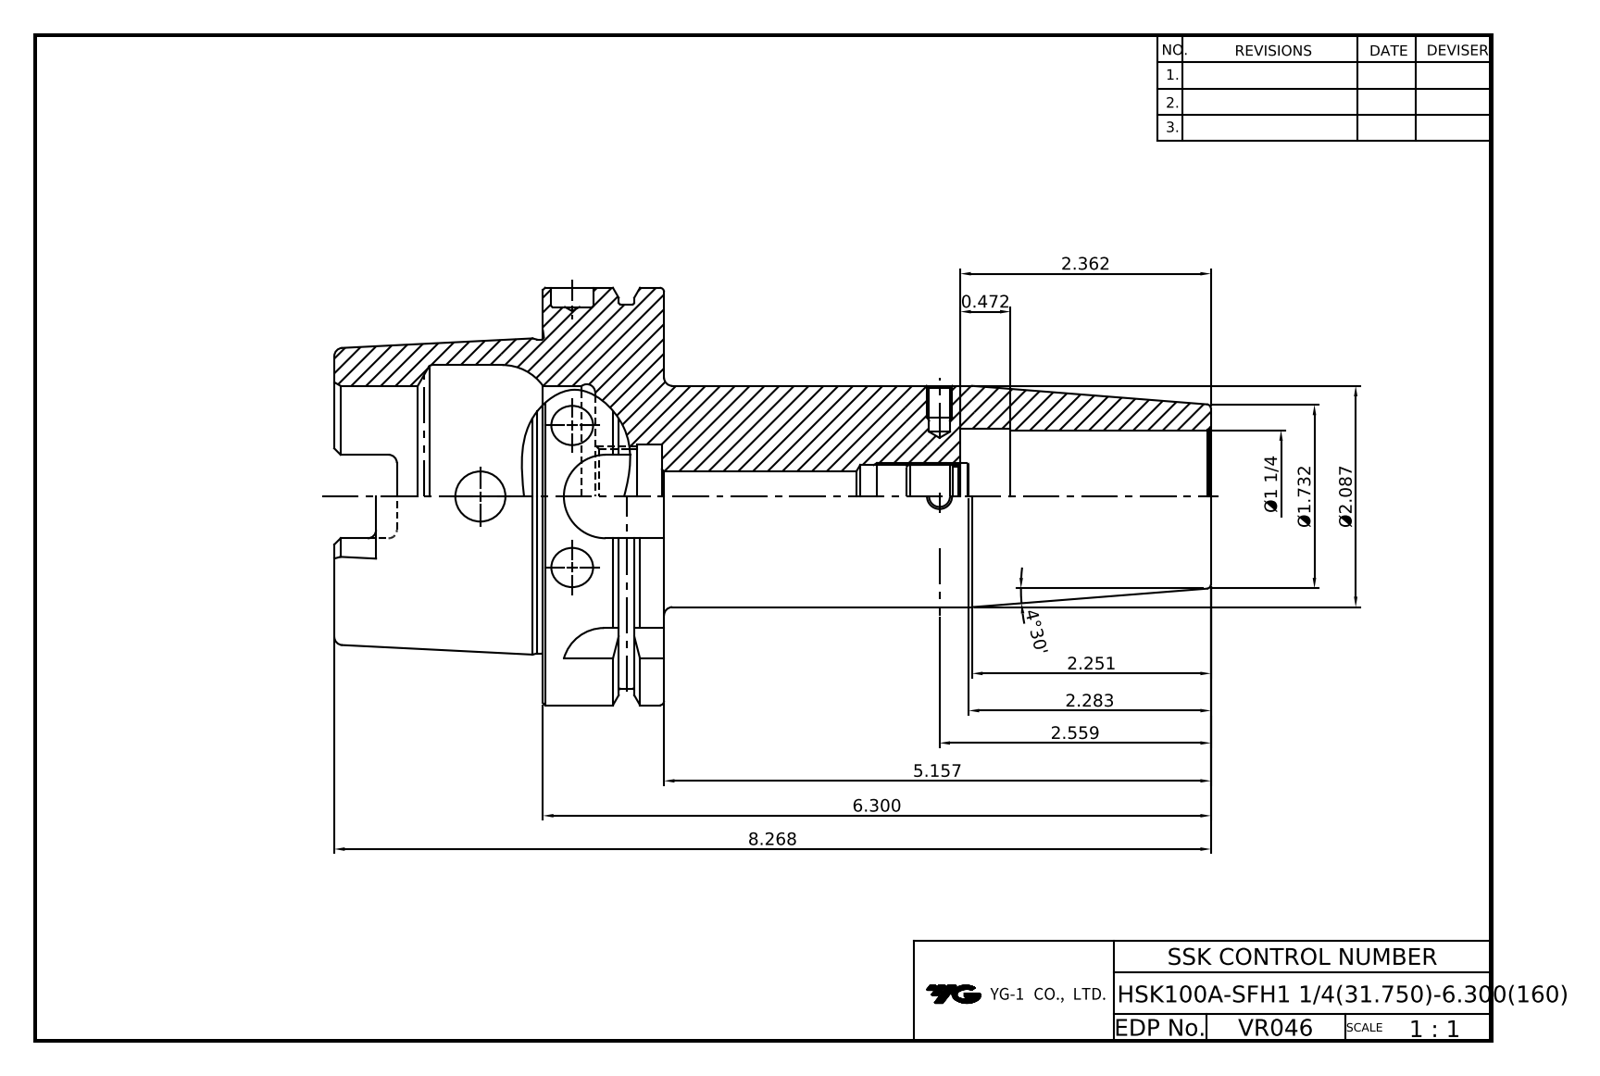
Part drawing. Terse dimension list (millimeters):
name: HSK100A-SFH31_75-160-3D
written by: CREO PARAMETRIC BY PTC INC, 2018400 (CONFIG_CONTROL_DESIGN)
unit: mm
bodies: 1 solid, 209 faces (55 planar, 68 cylindrical, 86 other)
size: 210 × 100 × 100
volume: 461 816 mm³; area: 81 257 mm²
holes: 2× ⌀5, 2× ⌀6, 2× ⌀12, 1× ⌀10, 1× ⌀15.1, 1× ⌀22.5, 1× ⌀24, 1× ⌀25, 1× ⌀31.75, 1× ⌀32.35, 1× ⌀53, 1× ⌀63.96
bosses: 1× ⌀100, 1× ⌀92, 1× ⌀75.16
rounds: 6× R2, 4× R4.88, 4× R10
face distances: 29, 12.5, 16.5, 62.5, 50, 79, 10, 150, 100, 87.5
hole spacings: 88, 110
